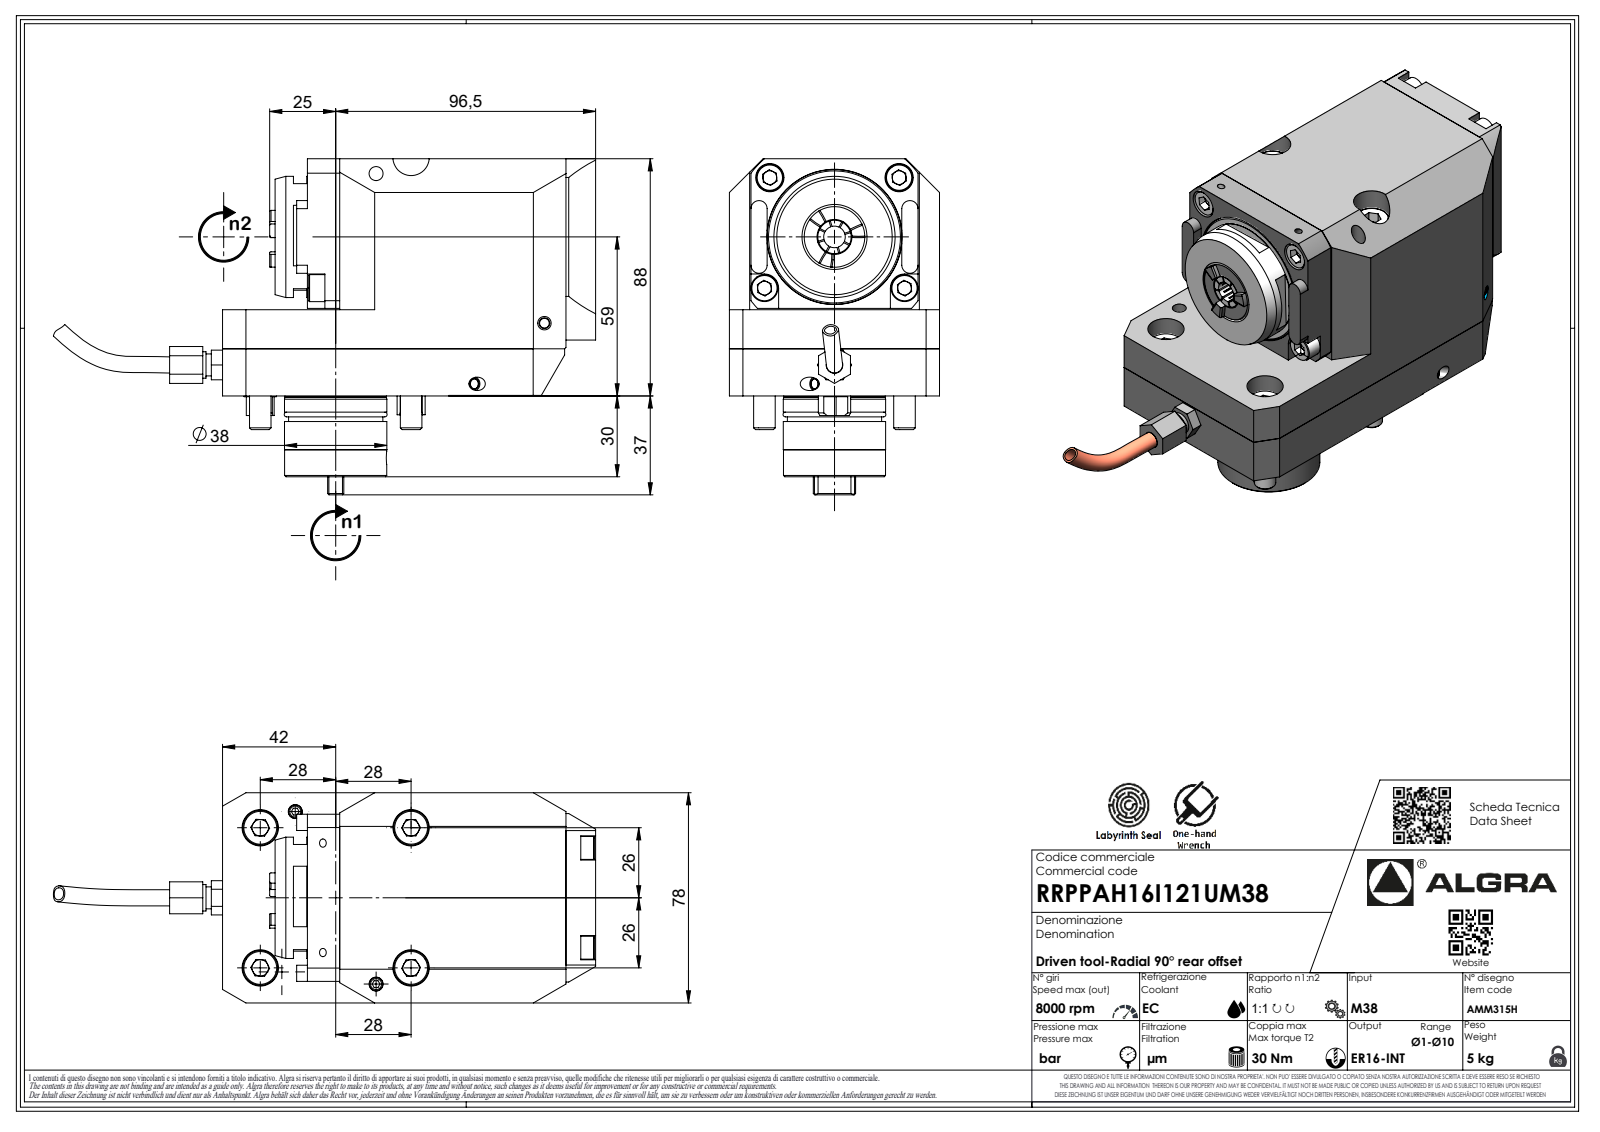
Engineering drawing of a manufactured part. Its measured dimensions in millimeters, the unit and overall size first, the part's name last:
Units: millimetres
Overall size (bounding box): 206.29 × 124.7 × 78
Round holes (diameter × count): ⌀2.1 ×1
Round bosses / shafts (diameter × count): ⌀8 ×4, ⌀45 ×1, ⌀38 ×1, ⌀37.9 ×1, ⌀37.6 ×1, ⌀35 ×1, ⌀12 ×1, ⌀9.8 ×1
Partial cylindrical surfaces — rounded edges, fillets, slot ends (radius × count): R0.33 ×7, R0.52 ×7, R3.7 ×7, R3 ×4, R0.21 ×1, R6 ×1, R6.5 ×1, R7.85 ×1
Main face-to-face distances: 78, 88, 56, 32, 31.8, 87.8, 138.5, 19.5, 12, 31.5
Volume: 798 296 mm³ · Surface area: 62 937 mm²
Bodies: 1 solid, 500 faces (343 planar, 58 cylindrical, 99 other)
Part name (STEP PRODUCT): RRPPAH16I121UM38
STEP written by: SolidWorks 2023 (AUTOMOTIVE_DESIGN)
